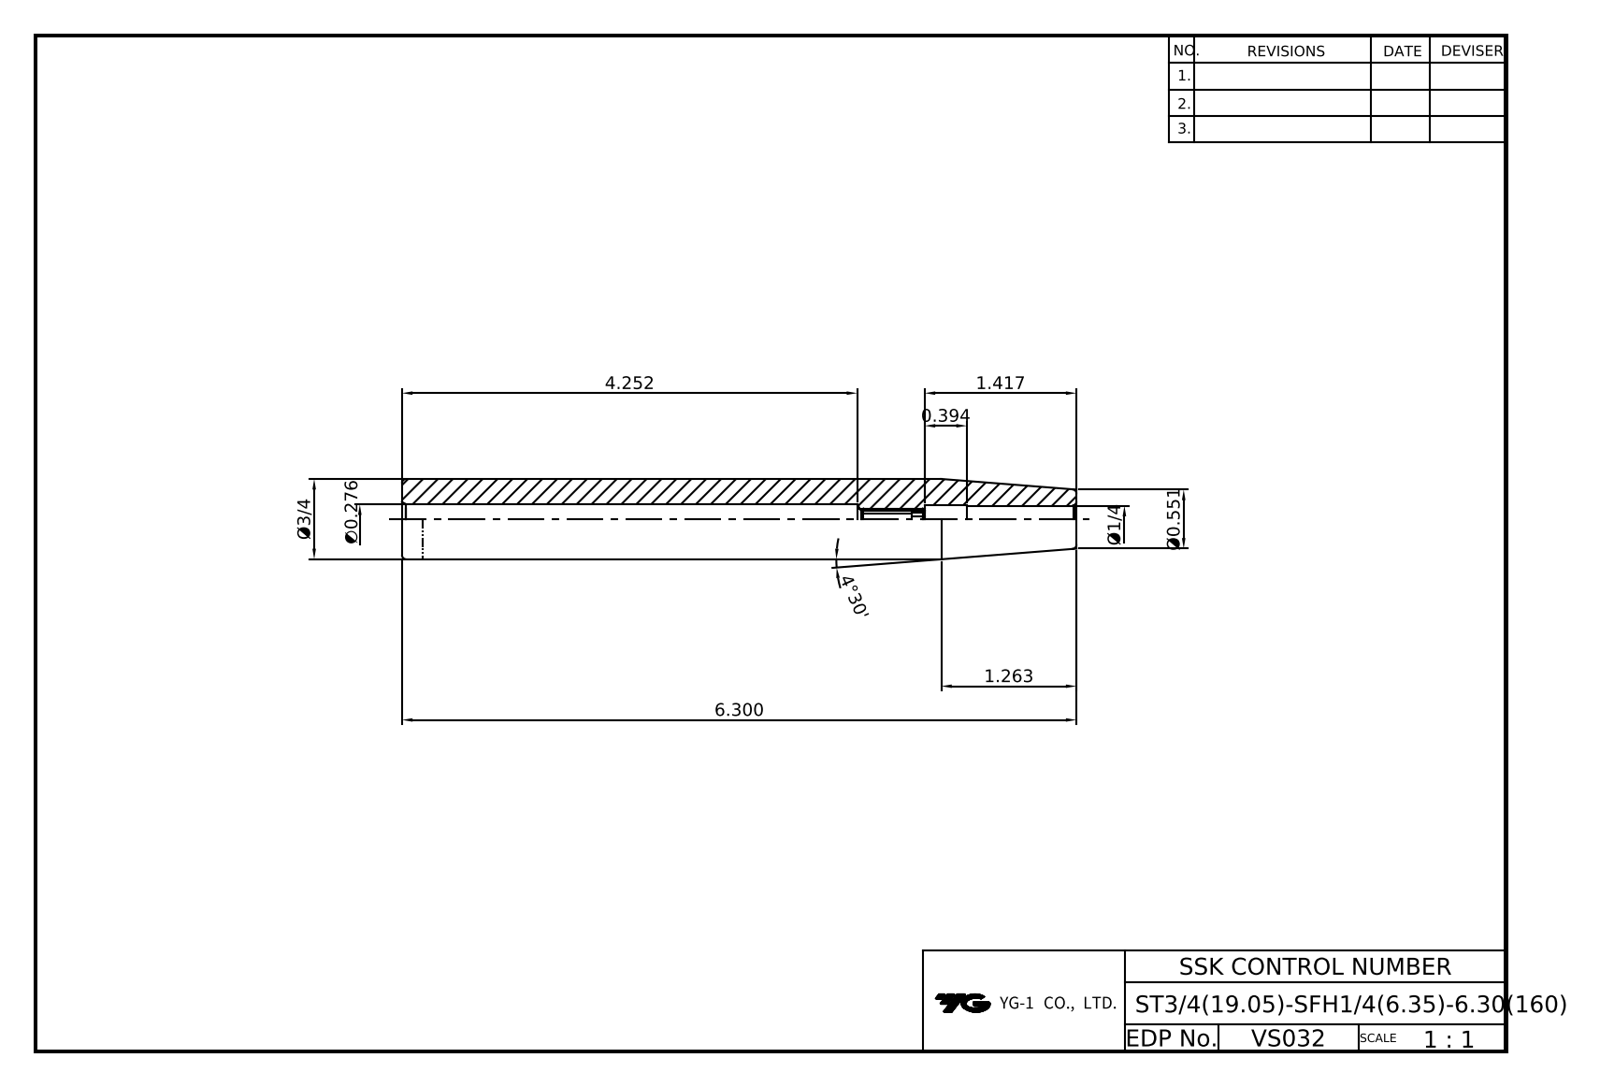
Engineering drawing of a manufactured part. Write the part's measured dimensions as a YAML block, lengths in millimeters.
part_name: "LO-ST19.05-SFH6.35-160"
step_written_by: "Autodesk Inventor 2024 (AUTOMOTIVE_DESIGN)"
units: millimeters
bodies: {solids: 1, faces: 14, planar: 4, cylindrical: 5, other: 5}
overall_size: [160, 19.05, 19.05]
volume: 37740
surface_area: 13035
round_holes:
  - {diameter: 4.13, count: 1}
  - {diameter: 6.35, count: 1}
  - {diameter: 7, count: 1}
  - {diameter: 7.35, count: 1}
round_bosses_or_shafts:
  - {diameter: 19.05, count: 1}
face_to_face_distances: [160, 124, 36, 134, 10, 26]
